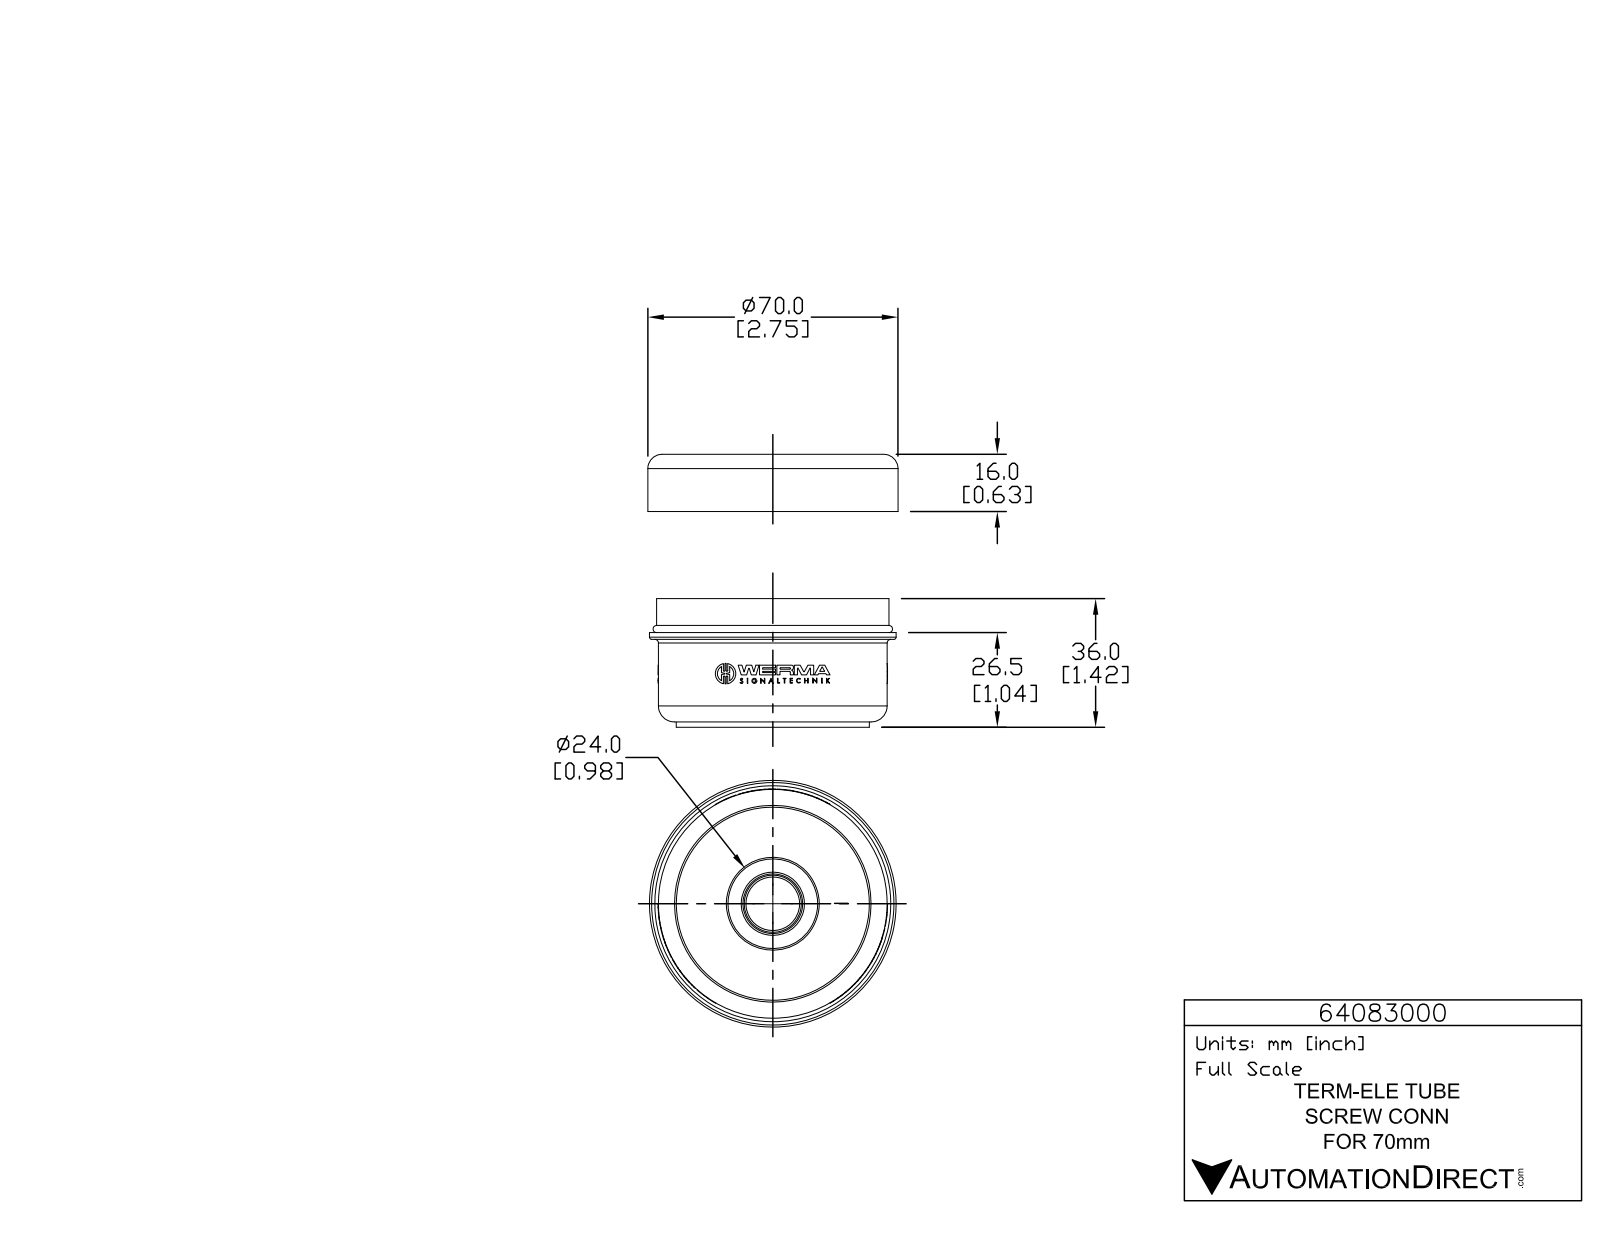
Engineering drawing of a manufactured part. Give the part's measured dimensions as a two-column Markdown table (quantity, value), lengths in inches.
| quantity | value |
| --- | --- |
| part name | 64083000 |
| STEP written by | SolidWorks 2015 (AUTOMOTIVE_DESIGN) |
| units | inches |
| bodies | 2 solids, 1069 faces (732 planar, 315 cylindrical, 22 other) |
| overall size | 2.756 × 2.756 × 1.732 |
| volume | 7.073 in³ |
| surface area | 52.18 in² |
| round holes (diameter × count) | 0.039 × 3, 0.236 × 2, 0.099 × 1, 0.169 × 1, 0.395 × 1, 0.591 × 1, 0.988 × 1, 1.024 × 1, 2.661 × 1, 2.701 × 1 |
| round bosses / shafts (diameter × count) | 0.226 × 3, 0.056 × 3, 2.756 × 1, 2.717 × 1, 2.559 × 1, 2.52 × 1, 2.126 × 1, 0.697 × 1 |
| partial cylindrical surfaces (radius × count) | 0.008 × 6, 0.008 × 6, 0.008 × 6, 0.131 × 6, 0.004 × 3, 0.005 × 3, 0.006 × 3, 0.008 × 3 |
| main face-to-face distances | 0.177, 0.079, 0.256, 1.476, 1.654, 1.732, 1.102, 0.374, 0.551, 0.63 |
| hole center spacings | 0.827, 0.02, 0.104, 0.388, 0.472, 0.572, 0.846, 0.917 |
